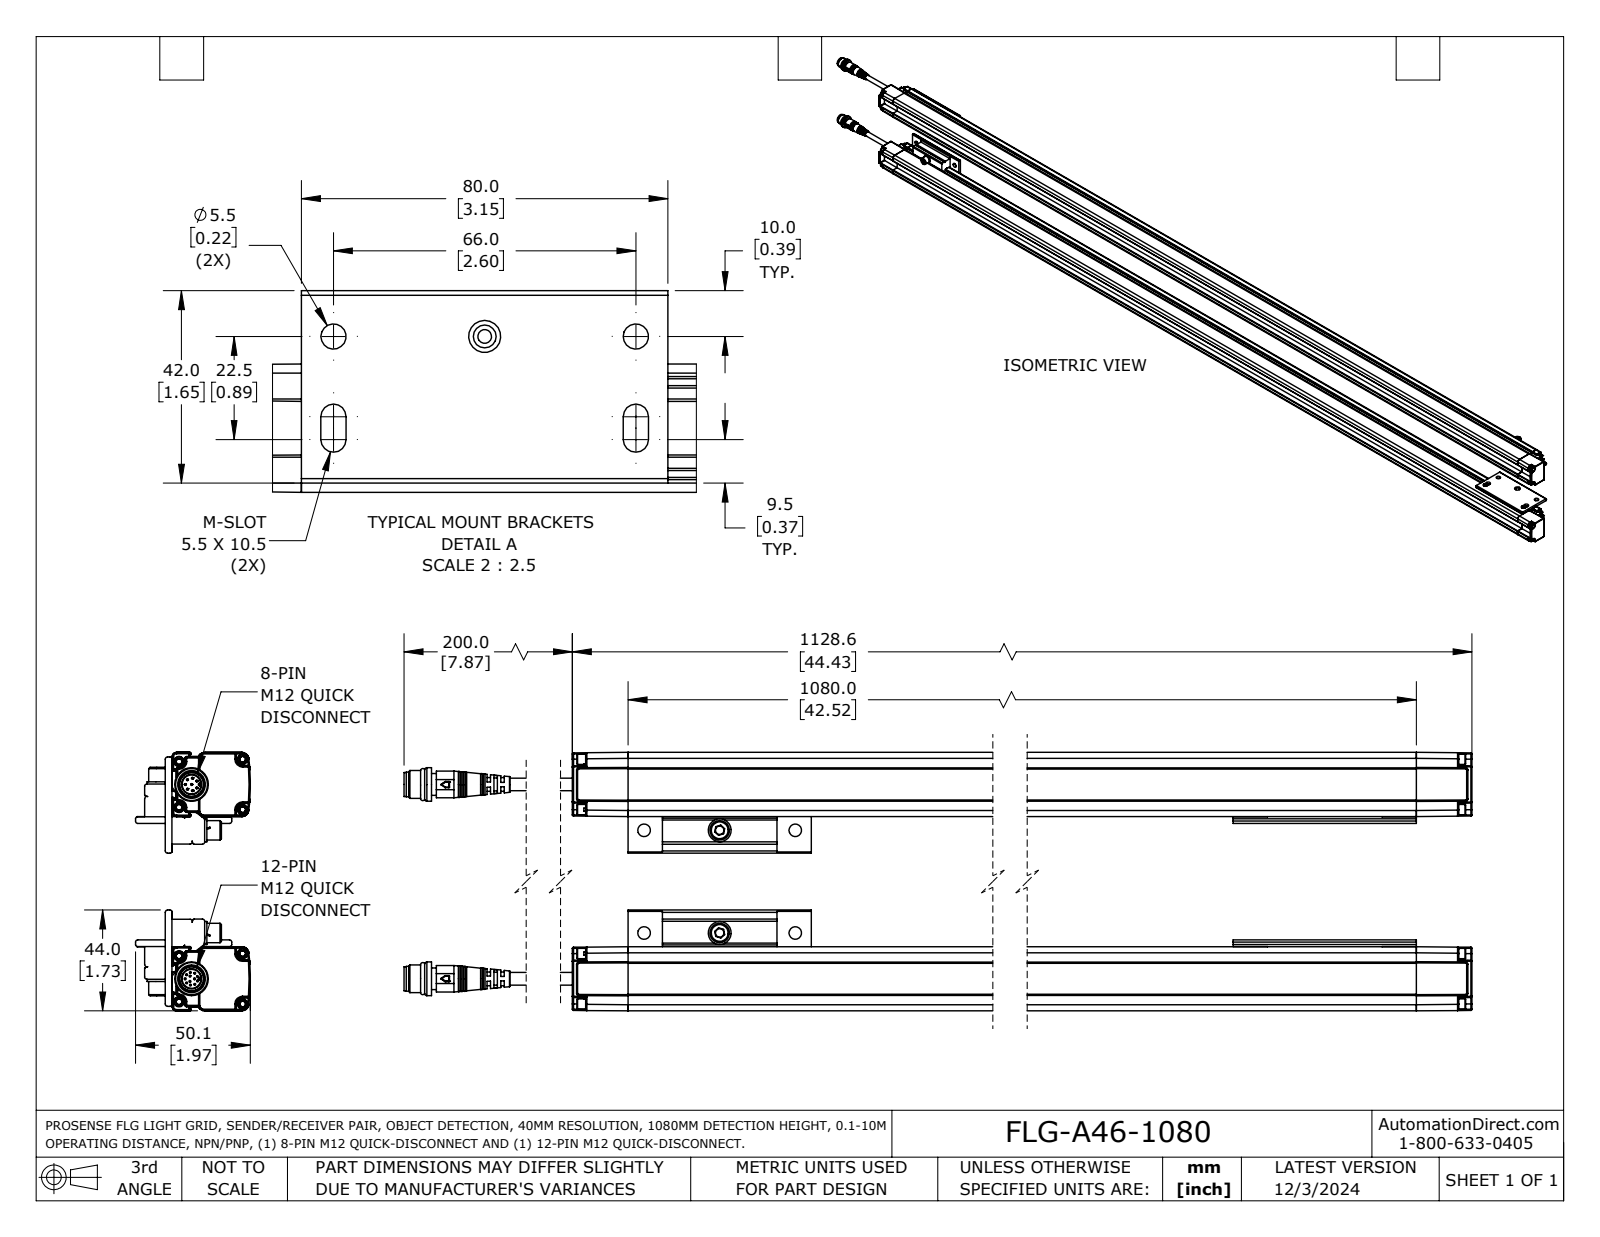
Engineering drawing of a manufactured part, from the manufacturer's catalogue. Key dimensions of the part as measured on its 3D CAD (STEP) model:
Part name (STEP PRODUCT): FLG-A46-1080
STEP written by: SolidWorks 2023 (AUTOMOTIVE_DESIGN)
Units: inches
Bodies: 5 solids, 869 faces (435 planar, 238 cylindrical, 196 other)
Overall size (bounding box): 48.053 × 1.972 × 1.732
Volume: 55.62 in³ · Surface area: 350.9 in²
Round holes (diameter × count): ⌀0.016 ×16, ⌀0.217 ×4, ⌀0.098 ×2, ⌀0.197 ×2, ⌀0.327 ×1
Round bosses / shafts (diameter × count): ⌀0.031 ×8, ⌀0.177 ×4, ⌀0.118 ×4, ⌀0.394 ×2, ⌀0.335 ×2, ⌀0.217 ×2, ⌀0.146 ×2, ⌀0.059 ×2
Partial cylindrical surfaces — rounded edges, fillets, slot ends (radius × count): R0.02 ×76, R0.039 ×20, R0.01 ×10, R0.108 ×8, R0.008 ×6, R0.012 ×6, R0.1 ×4, R0.049 ×2
Main face-to-face distances: 1.102, 0.071, 0.817, 0.285, 0.97, 1.041, 0.215, 1.031, 0.746, 0.531
Hole centre spacings: 0.108, 0.163, 1.299, 0.215, 0.089, 0.09, 0.09, 0.118
